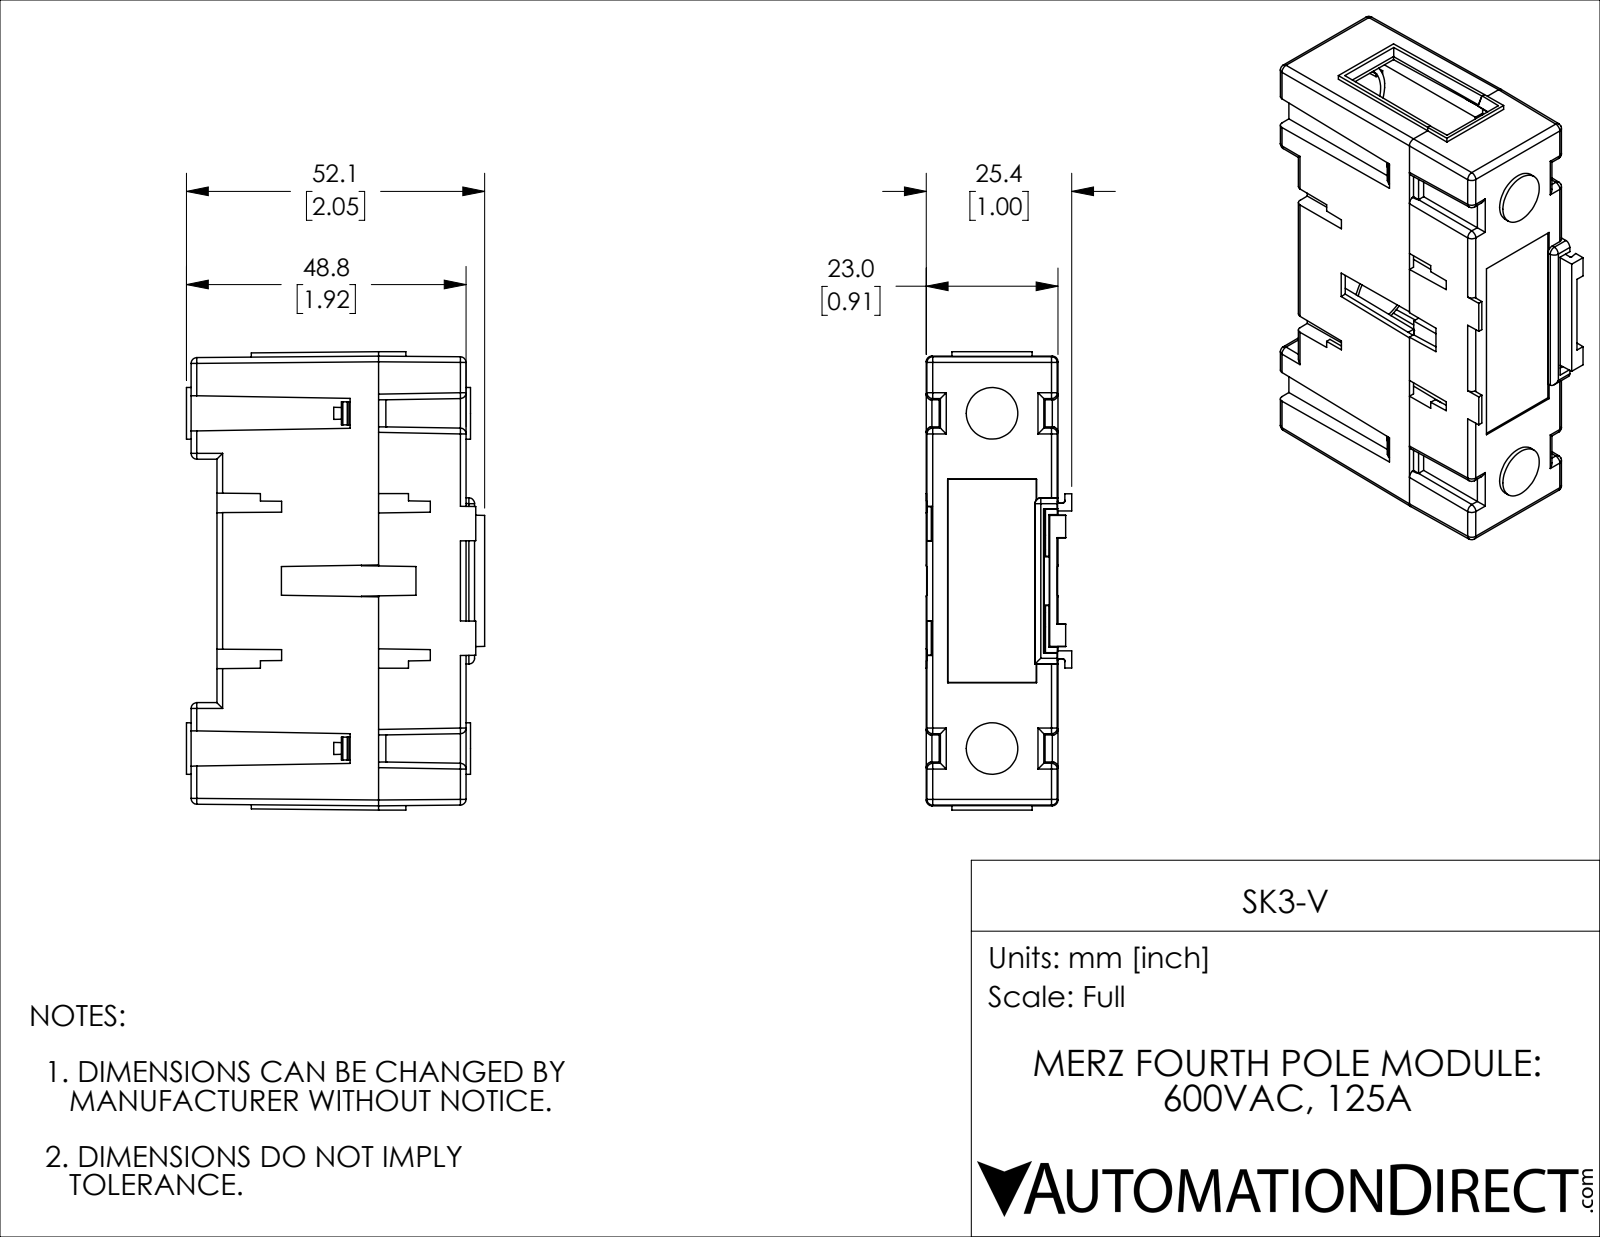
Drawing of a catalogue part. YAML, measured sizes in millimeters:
part_name: "SK3-V"
step_written_by: "SolidWorks 2019 (AUTOMOTIVE_DESIGN)"
units: millimeters
bodies: {solids: 1, faces: 849, planar: 655, cylindrical: 91, other: 103}
overall_size: [80, 52, 25.4]
volume: 22500
surface_area: 36340
round_bosses_or_shafts:
  - {diameter: 9, count: 2}
partial_cylinders:
  - {radius: 1, count: 42}
  - {radius: 0.5, count: 6}
  - {radius: 0.3, count: 4}
  - {radius: 2, count: 4}
  - {radius: 0.2, count: 1}
face_to_face_distances: [1, 23, 22, 3, 60.5, 0.7, 42.2, 18, 42.5, 18.6]
